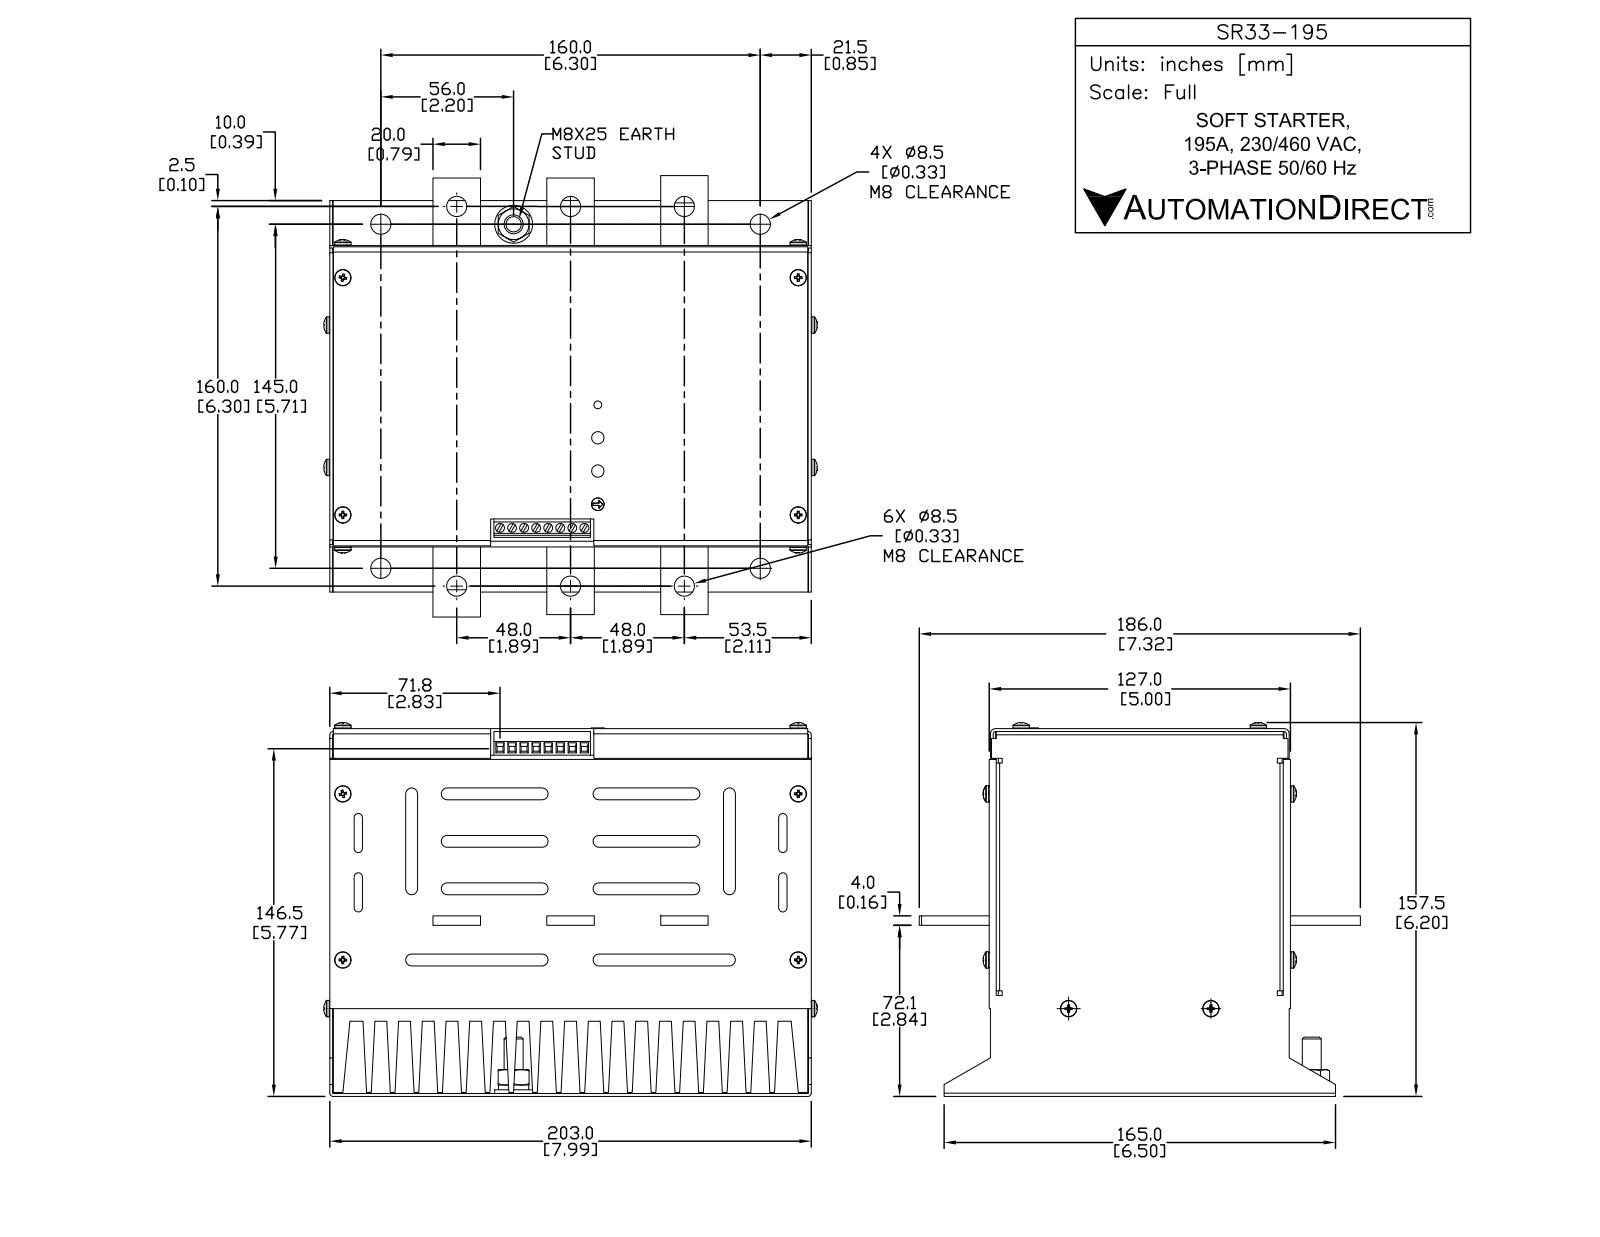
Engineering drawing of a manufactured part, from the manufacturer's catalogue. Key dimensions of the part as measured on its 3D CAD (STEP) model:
Part name (STEP PRODUCT): SR33-195
STEP written by: SolidWorks 2013 (AUTOMOTIVE_DESIGN)
Units: millimetres
Bodies: 1 solid, 881 faces (580 planar, 155 cylindrical, 146 other)
Overall size (bounding box): 203 × 186 × 158
Volume: 3 204 000 mm³ · Surface area: 529 358 mm²
Round holes (diameter × count): ⌀3.82 ×8, ⌀8.5 ×4
Round bosses / shafts (diameter × count): ⌀6.9 ×8, ⌀16 ×7, ⌀8.5 ×6, ⌀8 ×1
Partial cylindrical surfaces — rounded edges, fillets, slot ends (radius × count): R2.5 ×20, R1.75 ×8, R1 ×4, R2 ×2
Main face-to-face distances: 9.99, 19.98, 29.97, 39.96, 49.95, 59.94, 69.93, 79.92, 89.91, 99.9
Hole centre spacings: 4.92, 9.84, 14.76, 19.68, 24.6, 29.52, 145, 160
